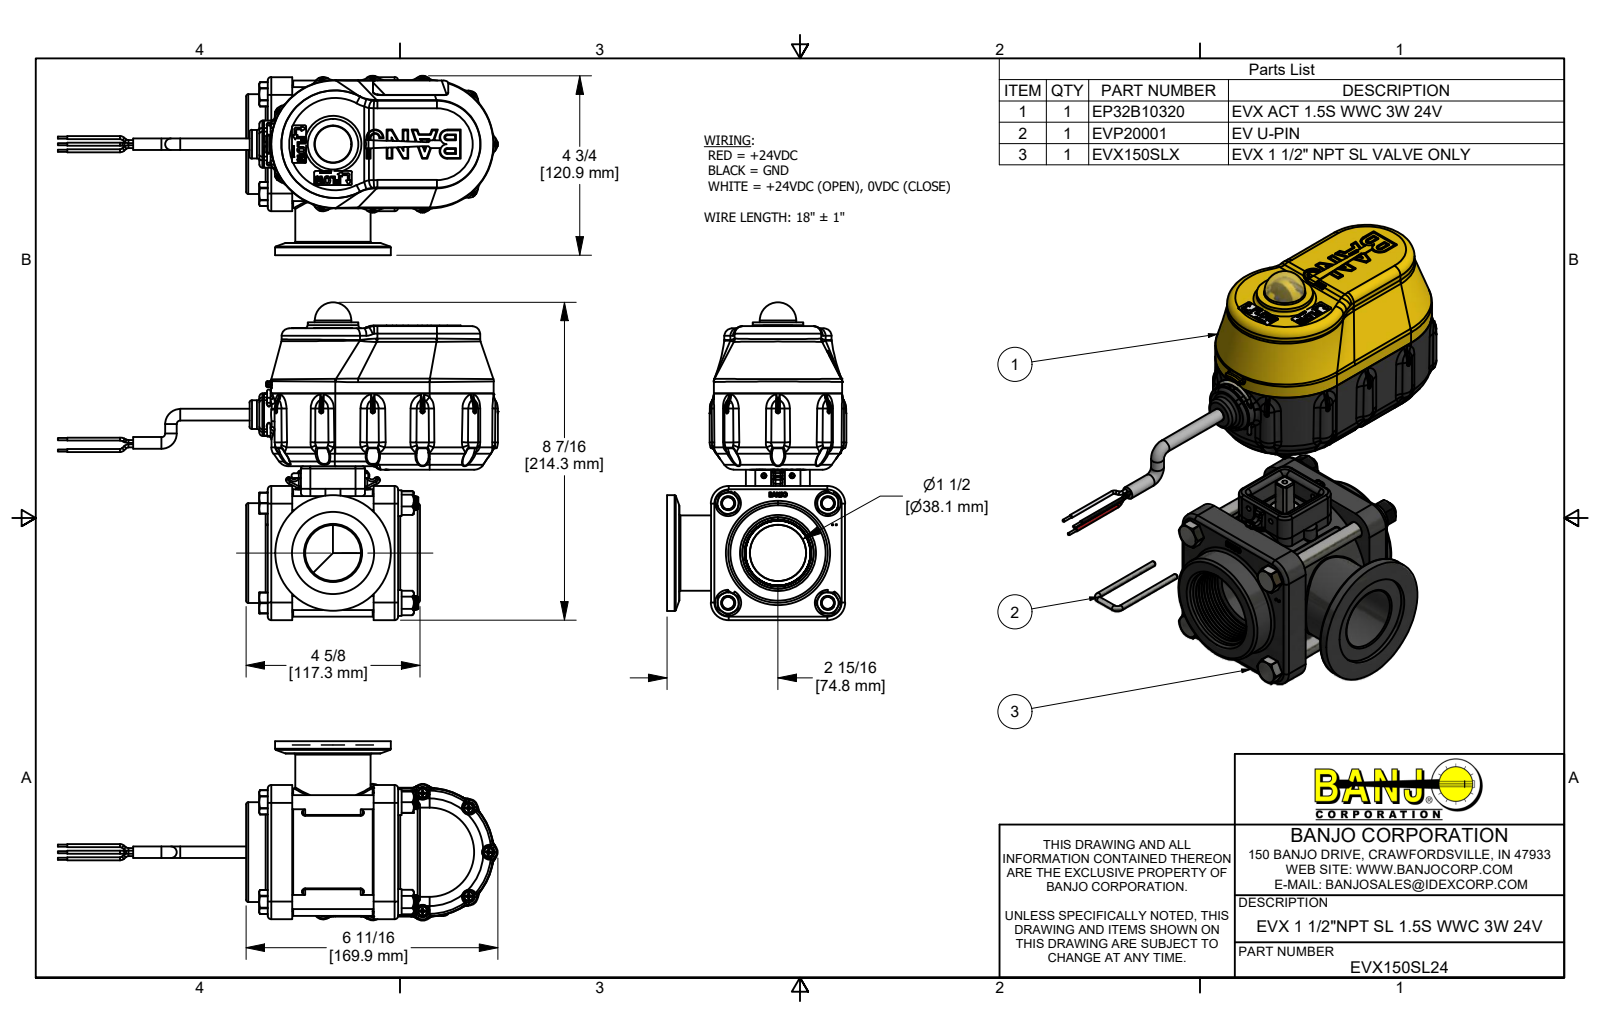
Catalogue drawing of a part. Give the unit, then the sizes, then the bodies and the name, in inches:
Units: inches
Overall size (bounding box): 11.685 × 8.437 × 4.76
Round holes (diameter × count): ⌀0.095 ×11, ⌀0.15 ×11, ⌀0.08 ×7, ⌀0.107 ×4, ⌀0.126 ×4, ⌀0.136 ×4, ⌀0.148 ×4, ⌀0.15 ×4, ⌀0.17 ×4, ⌀0.307 ×4, ⌀0.385 ×4, ⌀0.406 ×4
Round bosses / shafts (diameter × count): ⌀0.324 ×60, ⌀0.25 ×17, ⌀0.08 ×15, ⌀0.14 ×11, ⌀0.108 ×11, ⌀0.085 ×11, ⌀0.058 ×6, ⌀0.375 ×5
Partial cylindrical surfaces — rounded edges, fillets, slot ends (radius × count): R0.013 ×180, R0.04 ×145, R0.01 ×92, R0.02 ×80, R0.005 ×53, R0.03 ×30, R0.06 ×28, R0.08 ×28
Main face-to-face distances: 0.1, 2.565, 0.65, 2.808, 0.211, 0.06, 0.151, 0.125, 1.896, 1.836
Hole centre spacings: 1.872, 2.648, 2.656, 1.662, 1.774, 2.088, 2.69, 2.73
Volume: 65.43 in³ · Surface area: 672.9 in²
Bodies: 98 solids, 11857 faces (3274 planar, 3348 cylindrical, 5235 other)
Part name (STEP PRODUCT): EVX150SL24; EP32B10320; B61905PPHS; B632038PM (+8 more)
STEP written by: Autodesk Inventor 2019 (AUTOMOTIVE_DESIGN)
